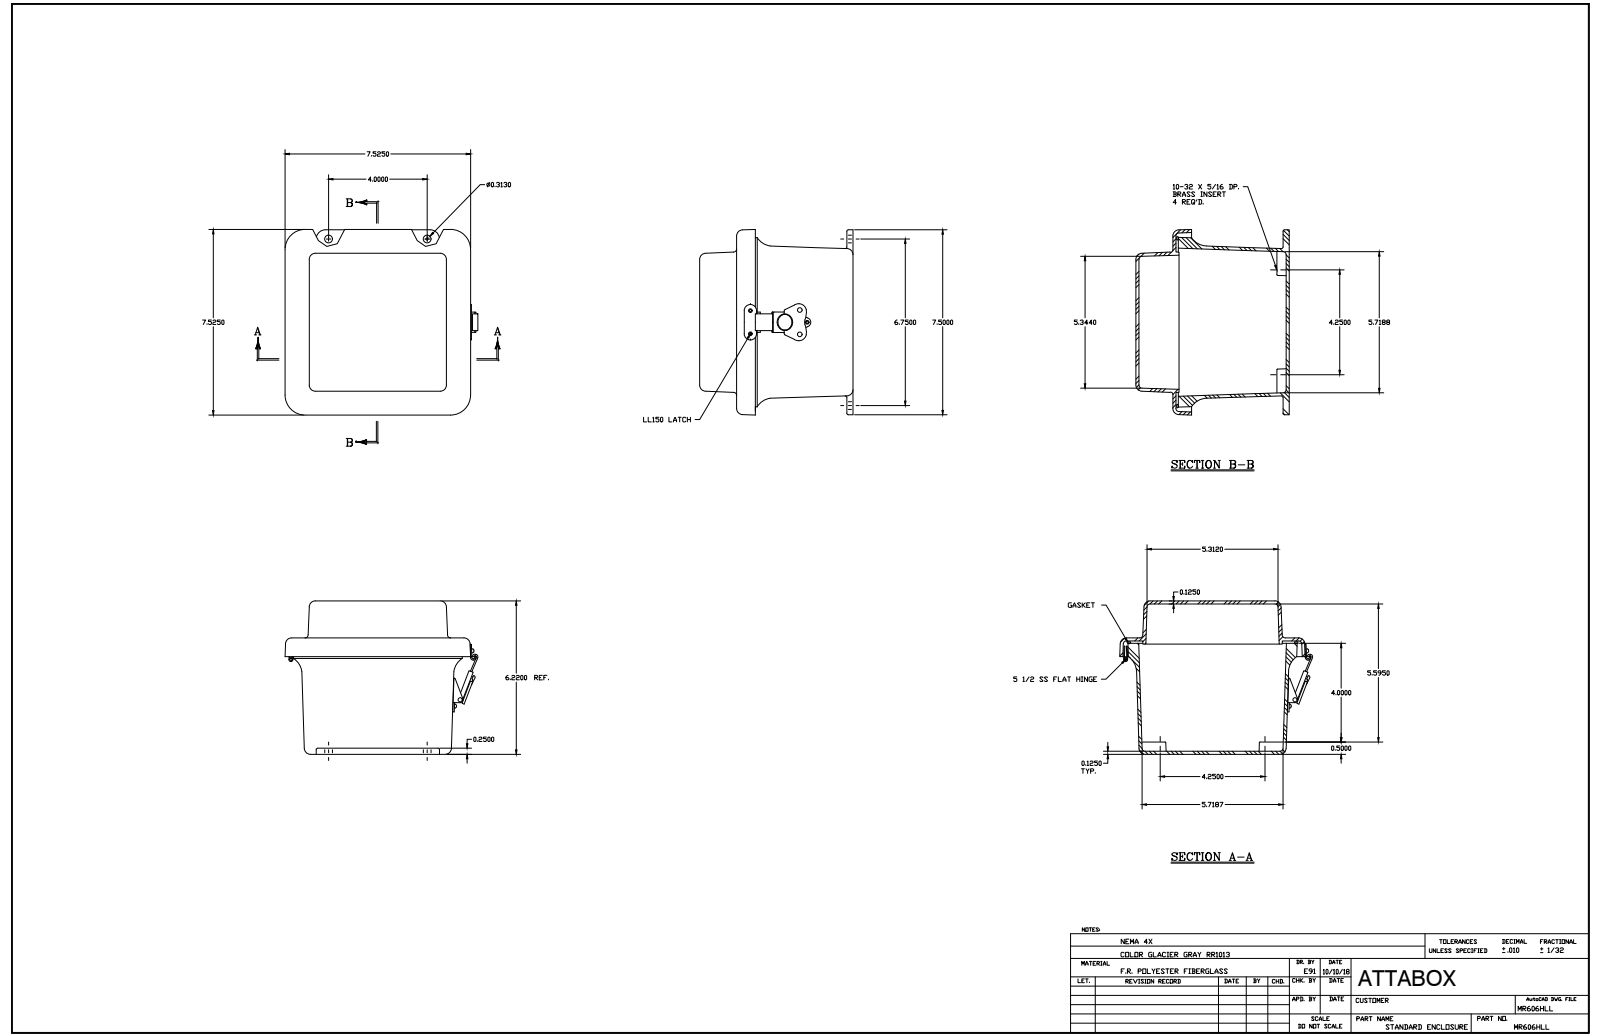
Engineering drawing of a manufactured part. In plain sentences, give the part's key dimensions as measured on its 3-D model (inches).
The part is named "MR606HLL". Its 3-D file was written by "SolidWorks 2018 (AUTOMOTIVE_DESIGN)". It is 30 solids with 779 faces: 315 planar, 294 cylindrical and 170 other. Overall it measures 7.629 by 7.525 by 6.338 inches. Its volume is 40.56 cubic inches and its surface area 579.3 square inches. Round holes: 9 of diameter 0.14, 5 of diameter 0.131, 5 of diameter 0.152, 4 of diameter 0.156, 4 of diameter 0.218, 2 of diameter 0.13, 2 of diameter 0.165, 2 of diameter 0.197, 1 of diameter 0.085, 1 of diameter 0.085, 1 of diameter 0.106, 1 of diameter 0.118. Round bosses or shafts: 9 of diameter 0.25, 5 of diameter 0.125, 4 of diameter 0.27, 4 of diameter 0.125, 1 of diameter 0.583, 1 of diameter 0.524, 1 of diameter 0.209, 1 of diameter 0.185. Partial cylindrical surfaces (rounded edges, fillets, slot ends): 20 of radius 0.031, 16 of radius 0.125, 16 of radius 0.25, 10 of radius 0.079, 4 of radius 0.037, 4 of radius 0.039, 4 of radius 0.045, 4 of radius 0.047. The main face-to-face distances are 0.125, 0.125, 1.5, 4.588, 6.088, 6.213, 6.338, 6.213, 4.713, 1.625. The hole center spacings are 5.308, 1.37, 2.5, 4.25, 6.187, 7.38, 0.469, 0.5.
